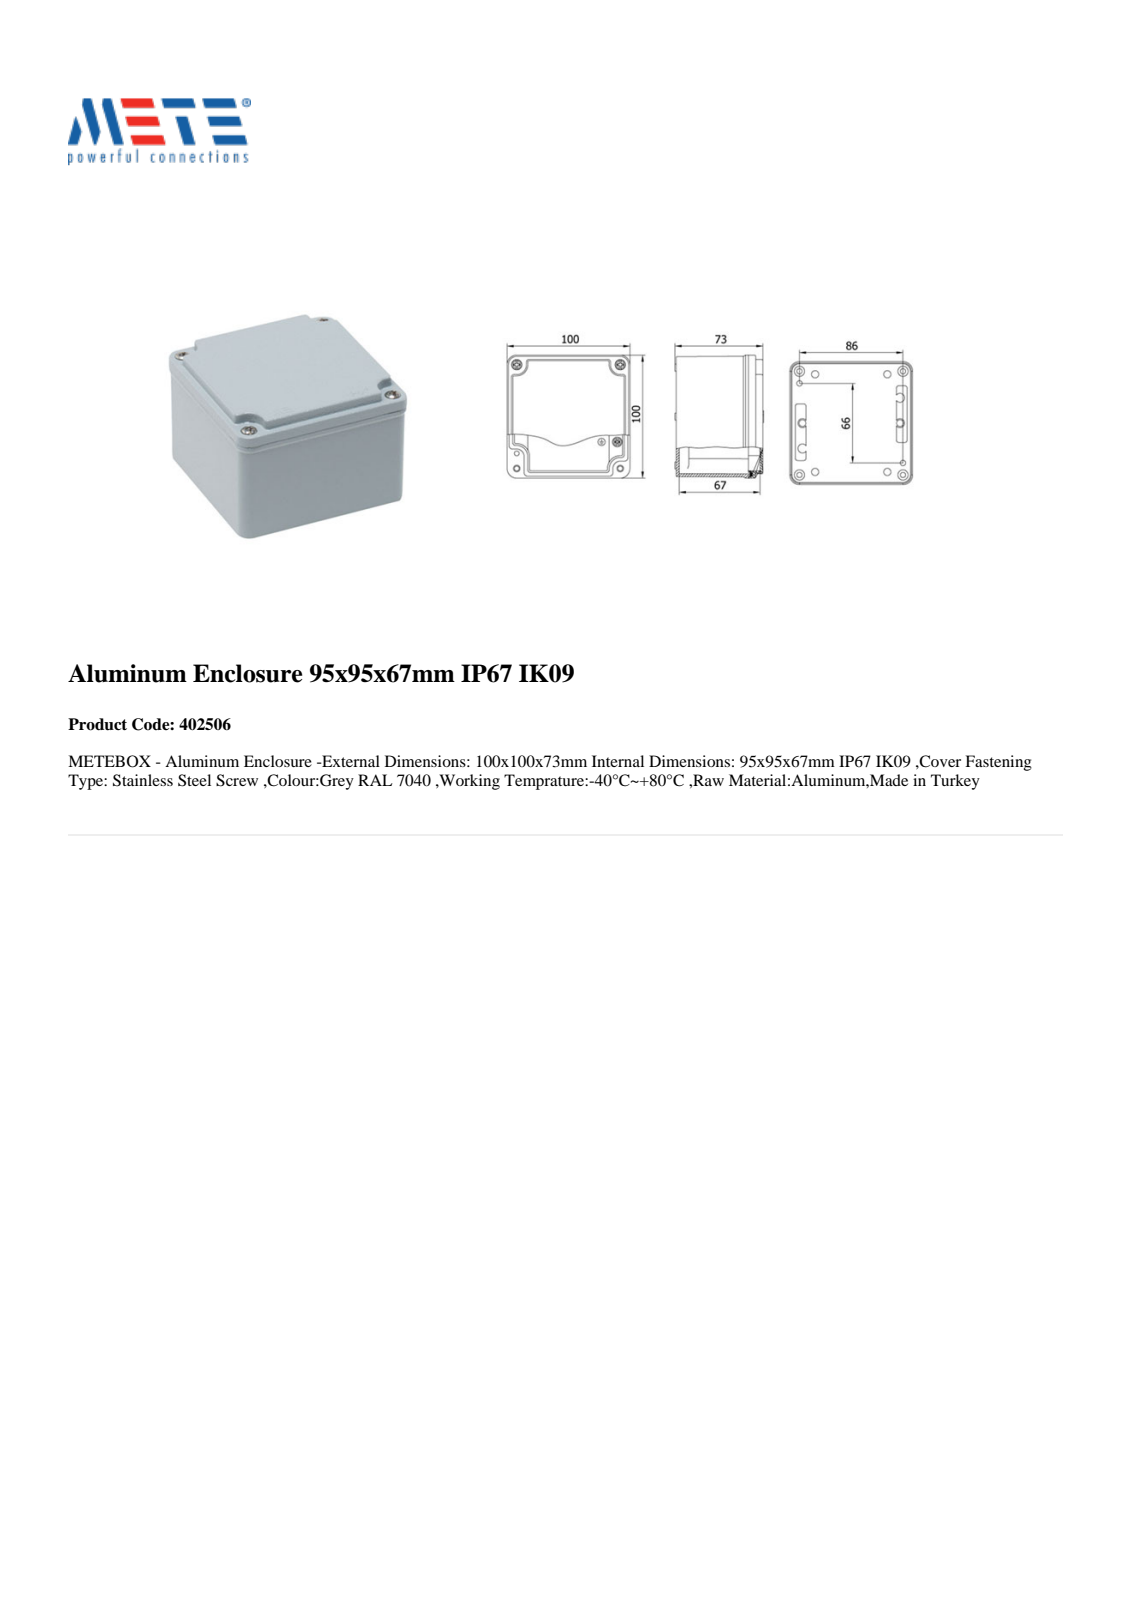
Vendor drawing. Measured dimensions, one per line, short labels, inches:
name: mtas15F42BE5odlc
written by: SIEMENS PLM Software NX 8.0 (AP203_CONFIGURATION_CONTROLLED_3D_DESIGN_OF_MECHANICAL_PARTS_AND_ASSEMBLIES_MIM_LF)
unit: in
bodies: 7 solids, 860 faces (243 planar, 257 cylindrical, 360 other)
size: 4.016 × 4.016 × 2.894
volume: 11.14 in³; area: 146.8 in²
holes: 4× ⌀0.119, 4× ⌀0.217, 4× ⌀0.343, 2× ⌀0.126
bosses: 6× ⌀0.236, 4× ⌀0.157, 1× ⌀0.315, 1× ⌀0.151, 1× ⌀0.118
rounds: 79× R0.008, 64× R0.004, 34× R0.039, 8× R0.079, 6× R0.106, 4× R0.02, 4× R0.248, 4× R0.276
face distances: 0.098, 2.736, 2.835, 2.638, 0.374, 2.362, 0.472, 2.264, 0.492, 0.591
hole spacings: 0.827, 0.872, 1.696, 2.522, 3.294, 3.386, 3.4, 3.698
